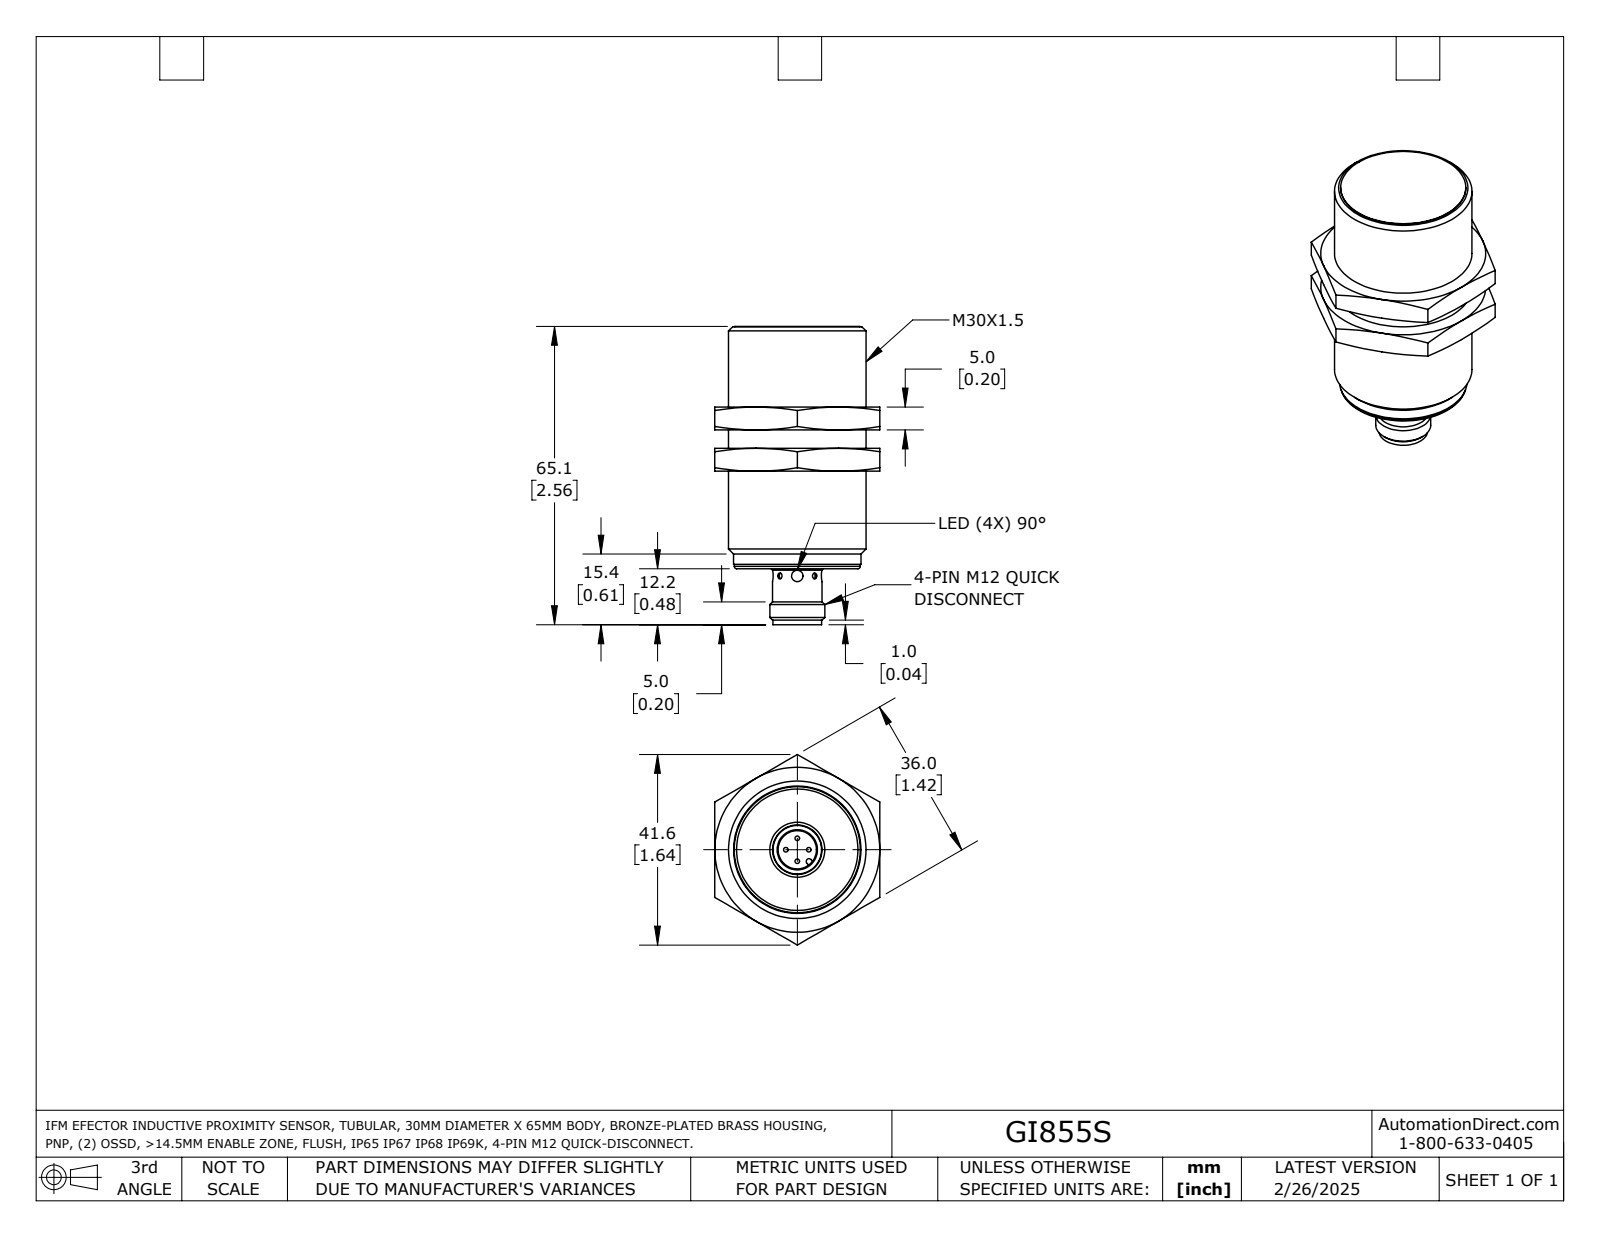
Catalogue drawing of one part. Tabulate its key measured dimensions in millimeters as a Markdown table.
| quantity | value |
| --- | --- |
| part name | GI855S |
| STEP written by | SolidWorks 2024 (AUTOMOTIVE_DESIGN) |
| units | millimeters |
| bodies | 3 solids, 88 faces (26 planar, 27 cylindrical, 35 other) |
| overall size | 65.11 × 41.57 × 36 |
| volume | 42 323 mm³ |
| surface area | 10 768 mm² |
| round holes (diameter × count) | 1.3 × 2, 2.5 × 2, 8.35 × 1, 28.38 × 1 |
| round bosses / shafts (diameter × count) | 30 × 1, 27.8 × 1, 27.5 × 1, 27.32 × 1, 12 × 1, 10.8 × 1, 10.6 × 1 |
| partial cylindrical surfaces (radius × count) | 0.6 × 1, 4.95 × 1 |
| main face-to-face distances | 9, 5, 36, 52.88, 21.27, 30.27, 31.61, 22.61, 26.27, 35.27 |
